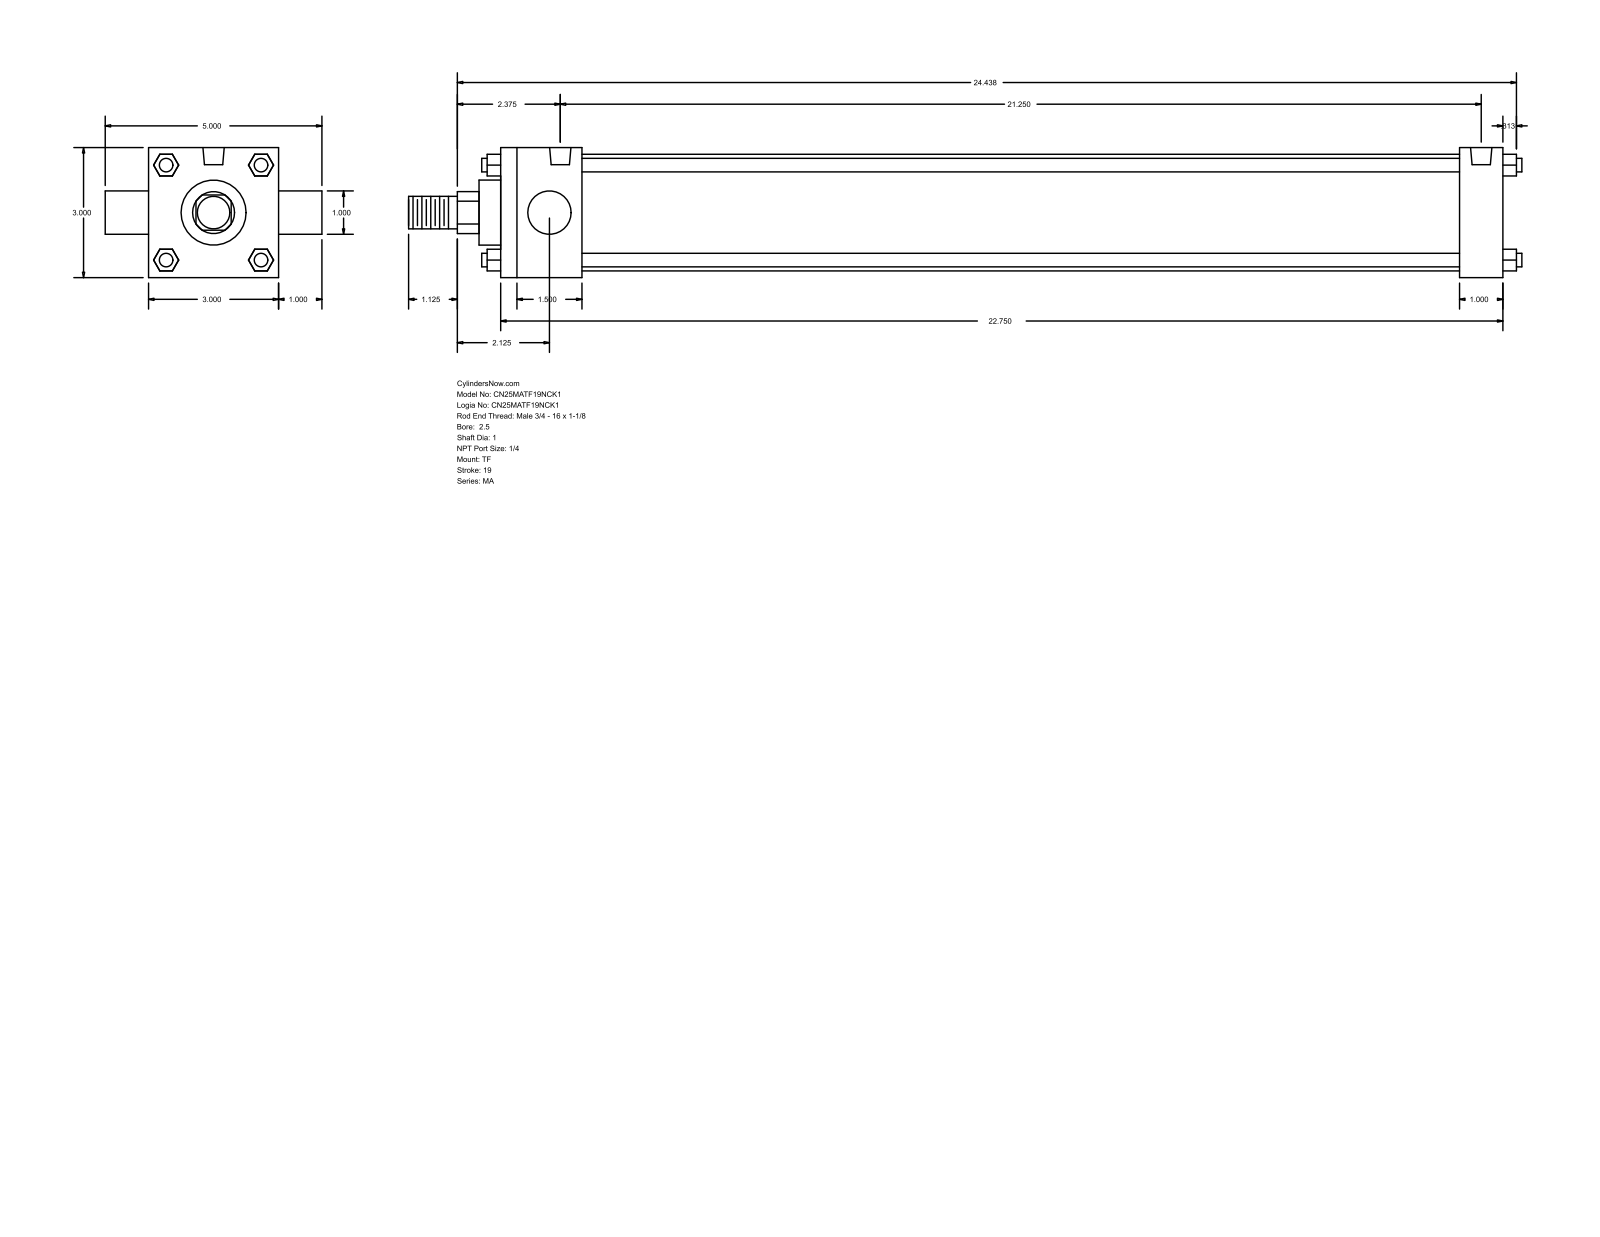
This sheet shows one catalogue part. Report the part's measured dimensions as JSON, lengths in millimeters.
{"part_name": "MA_TF__0250_1", "step_written_by": "GSSL Pune (CONFIG_CONTROL_DESIGN)", "units": "millimeters", "bodies": {"solids": 0, "faces": 120, "planar": 92, "cylindrical": 28, "other": 0}, "overall_size": [652.46, 127, 76.2], "round_holes": [[7.94, 3], [12.49, 2]], "round_bosses_or_shafts": [[7.94, 4], [25.4, 2], [68.33, 1], [38.1, 1], [19.05, 1]], "partial_cylinders_radius": [[12.29, 1]], "face_to_face_distances": [76.2, 587.37, 12.7, 47.63, 561.98, 514.35, 539.74, 25.39, 101.6, 25.4], "hole_center_spacings": [539.75]}
